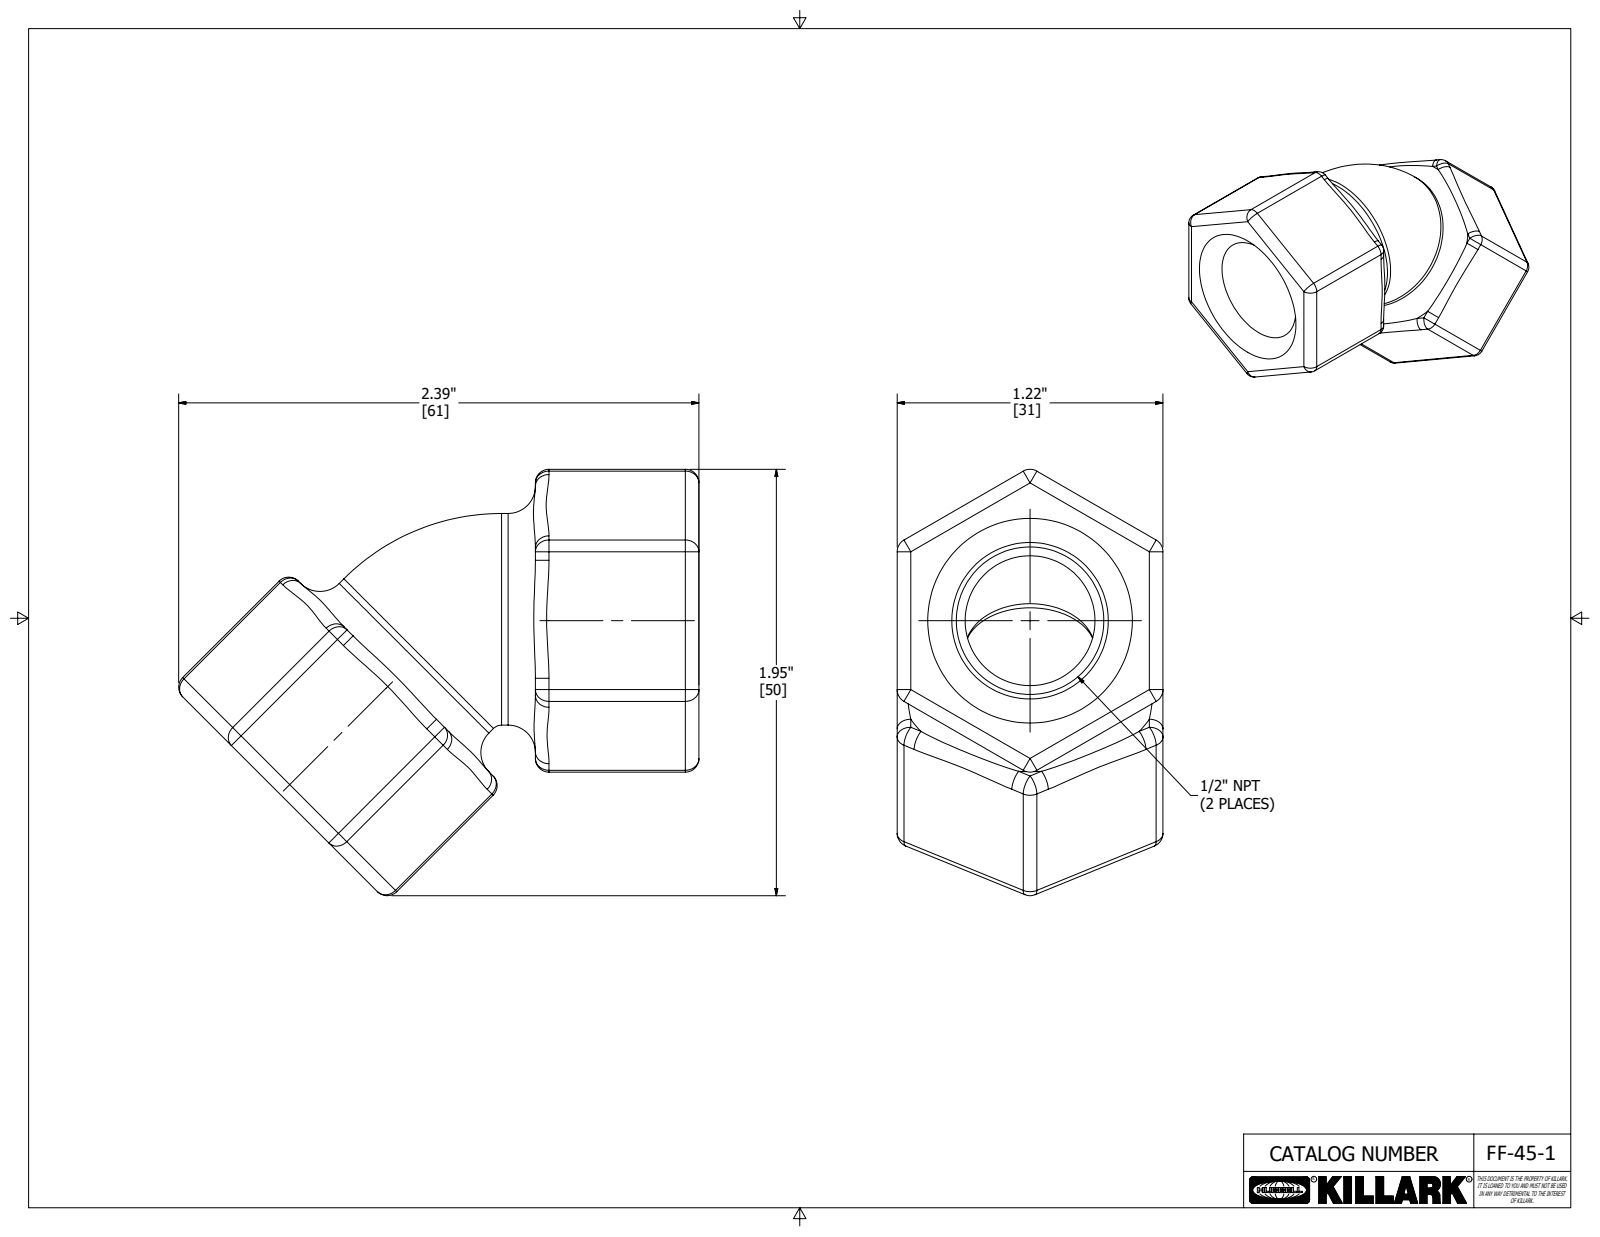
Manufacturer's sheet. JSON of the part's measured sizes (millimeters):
{"part_name": "FF-45-1", "step_written_by": "Autodesk Inventor 2020 (AUTOMOTIVE_DESIGN)", "units": "millimeters", "bodies": {"solids": 1, "faces": 122, "planar": 26, "cylindrical": 50, "other": 46}, "overall_size": [60.6, 49.6, 31], "volume_mm3": 26860, "surface_area_mm2": 9794, "round_bosses_or_shafts": [[24.6, 2]], "partial_cylinders_radius": [[1.6, 36]], "face_to_face_distances": [31, 30.9, 19.1]}
